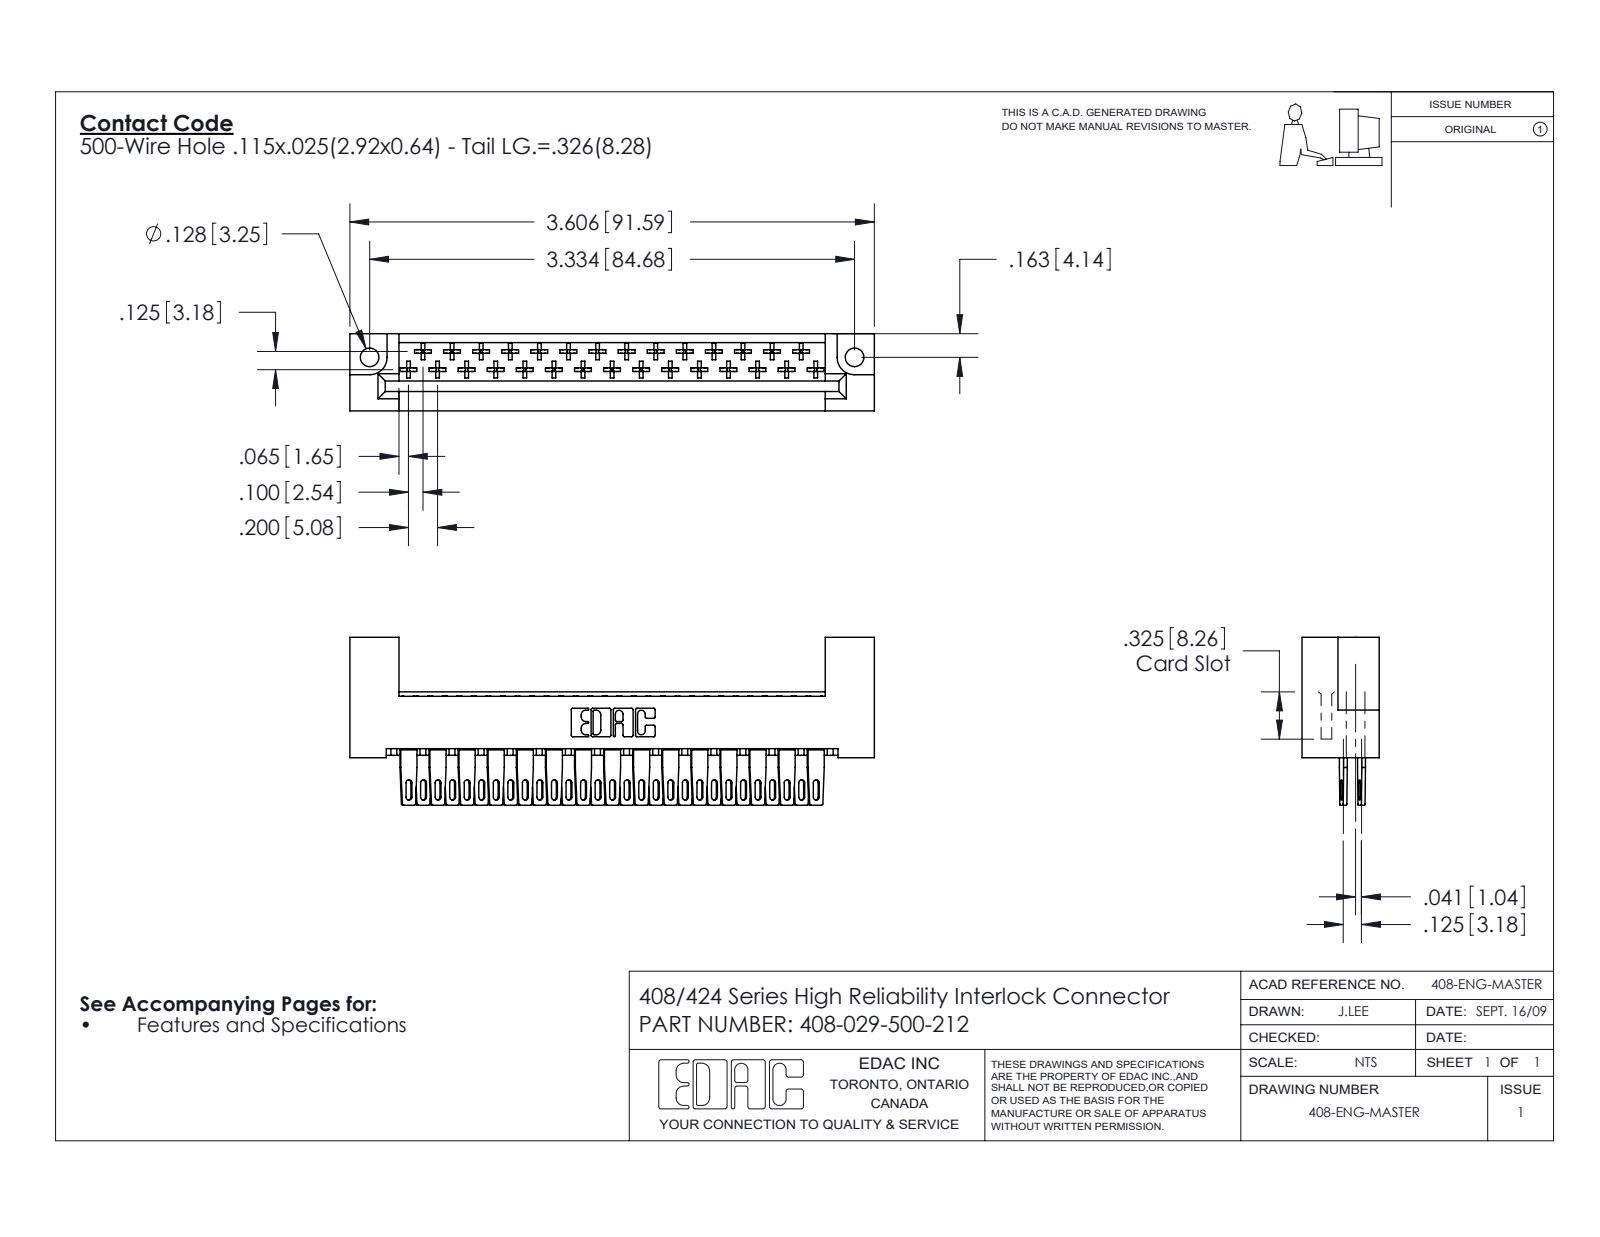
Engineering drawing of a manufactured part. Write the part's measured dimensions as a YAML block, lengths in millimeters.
part_name: "408-290-001_408-290-100; 408 Part_029 - 2; 408-029-500-212"
step_written_by: "SolidWorks 2016 (CONFIG_CONTROL_DESIGN)"
units: millimeters
bodies: {solids: 30, faces: 1792, planar: 1278, cylindrical: 398, other: 116}
overall_size: [91.6, 29.3, 13.5]
volume: 11900
surface_area: 14290
round_holes:
  - {diameter: 3.3, count: 2}
partial_cylinders:
  - {radius: 0.3, count: 232}
  - {radius: 0.5, count: 58}
  - {radius: 0.5, count: 31}
  - {radius: 0.3, count: 22}
  - {radius: 0.2, count: 6}
  - {radius: 0.8, count: 6}
  - {radius: 0.7, count: 3}
  - {radius: 3, count: 2}
face_to_face_distances: [13.5, 3.2, 2.5, 0.6, 0.6, 9.2, 8.3, 6, 6.6, 5.5]
hole_center_spacings: [84.7]
